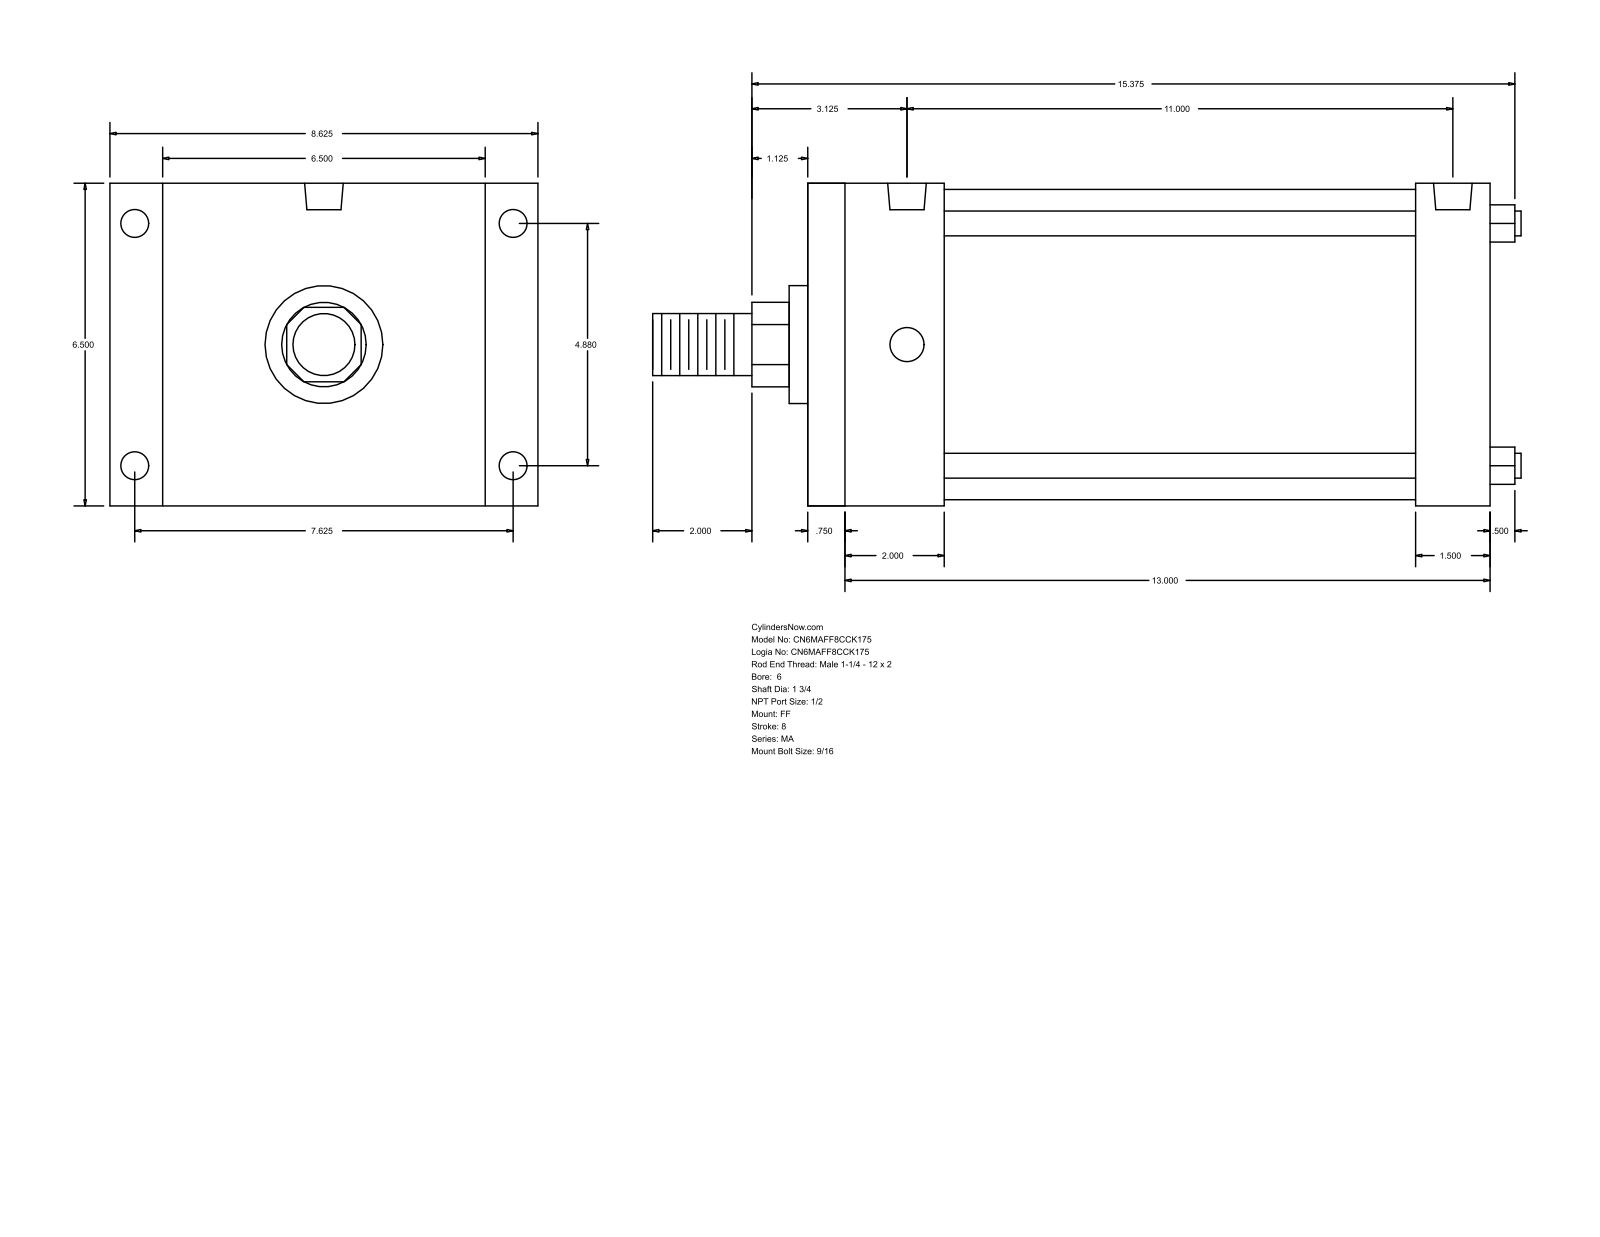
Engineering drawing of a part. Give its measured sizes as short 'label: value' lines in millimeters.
name: MA_FF__0600_1.75
written by: GSSL Pune (CONFIG_CONTROL_DESIGN)
unit: mm
bodies: 0 solids, 92 faces (64 planar, 28 cylindrical, 0 other)
size: 444.5 × 219.07 × 165.1
holes: 4× ⌀14.29, 4× ⌀17.46, 2× ⌀19.77
bosses: 4× ⌀12.7, 1× ⌀158.75, 1× ⌀60.33, 1× ⌀44.45, 1× ⌀31.75
rounds: 1× R21.63
face distances: 165.1, 349.25, 19.05, 330.2, 69.85, 50.8, 279.4, 311.16, 292.11, 241.31
hole spacings: 123.96, 193.68, 229.95, 279.39
